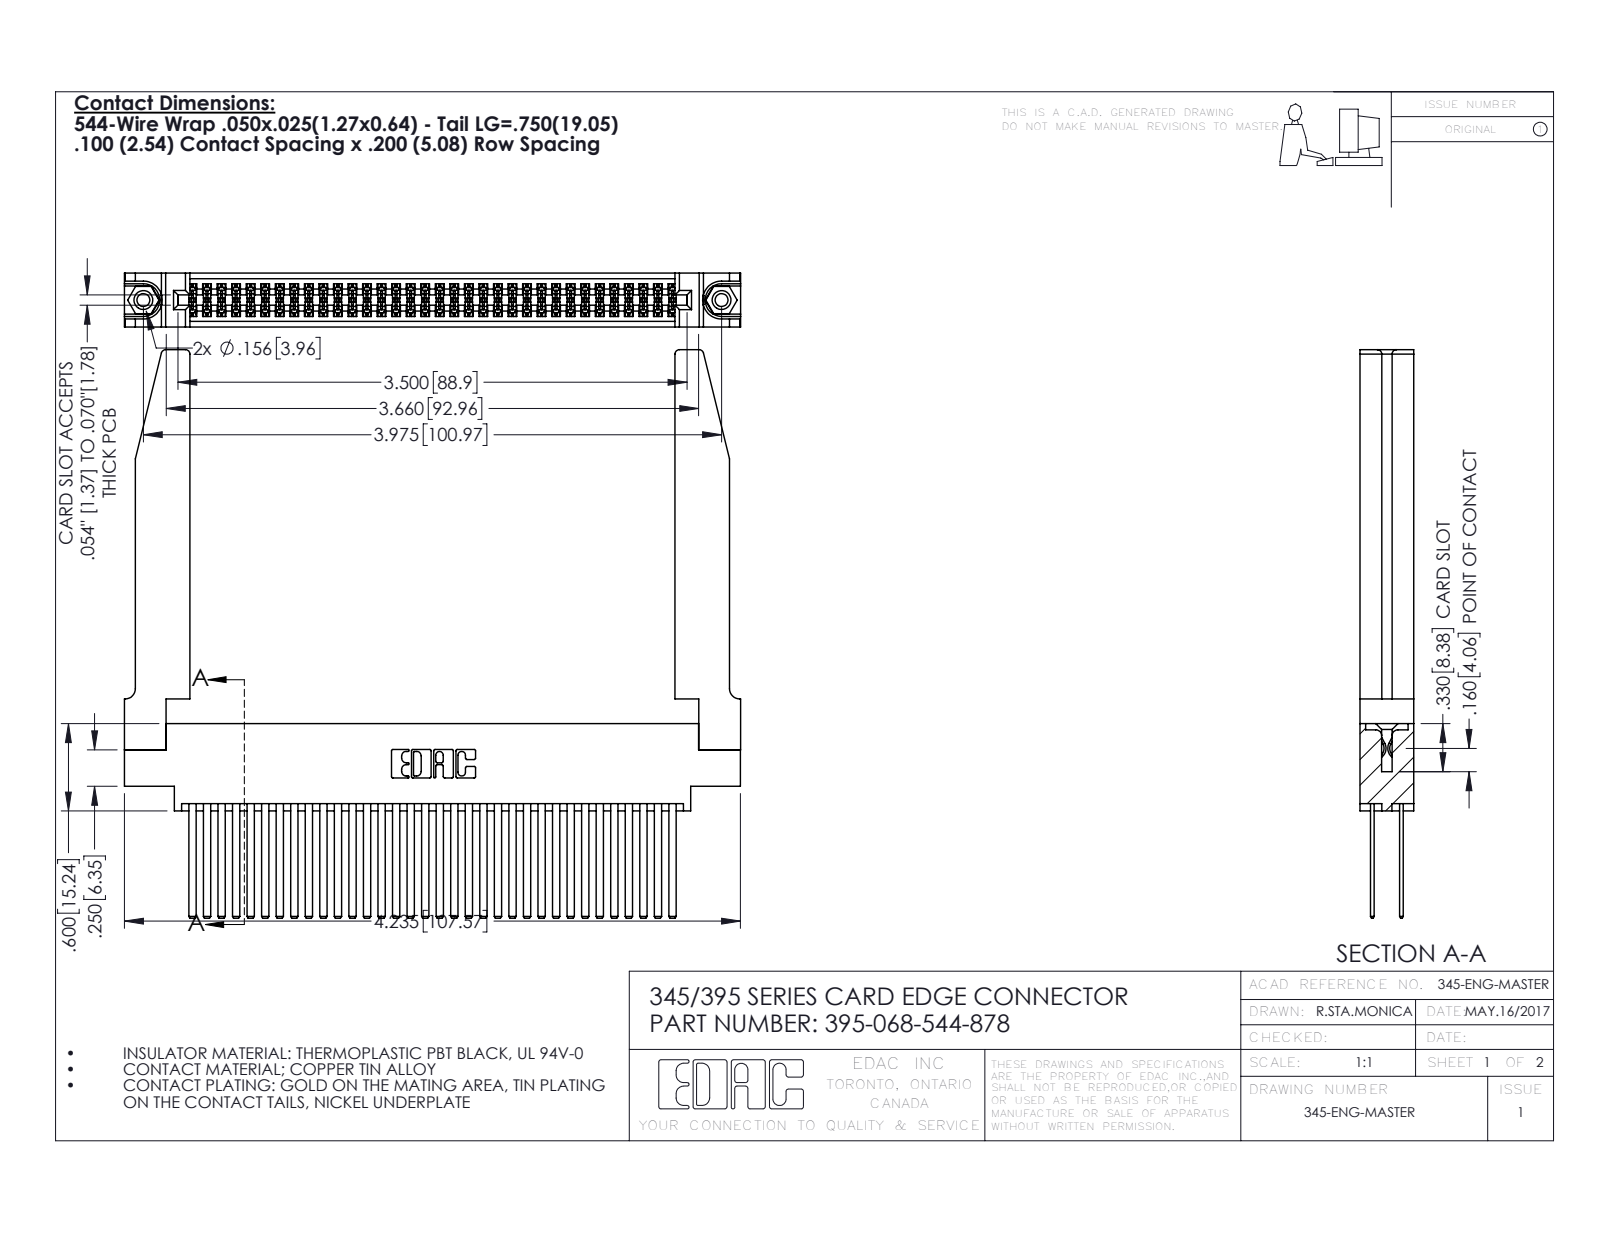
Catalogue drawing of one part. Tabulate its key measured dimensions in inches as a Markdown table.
| quantity | value |
| --- | --- |
| part name | 395-068-544-878; 345 Part_0.170 Offset - 0.156 Dia-TH; 345-292-001_345-293-144; 345-220-078_345-220-078 (+1 more) |
| STEP written by | SolidWorks 2016 (CONFIG_CONTROL_DESIGN) |
| units | inches |
| bodies | 73 solids, 3356 faces (2198 planar, 1106 cylindrical, 52 other) |
| overall size | 4.236 × 3.907 × 0.37 |
| volume | 1.159 in³ |
| surface area | 40.61 in² |
| round holes (diameter × count) | 0.089 × 2, 0.125 × 2, 0.156 × 2, 0.064 × 1 |
| round bosses / shafts (diameter × count) | 0.155 × 2 |
| partial cylindrical surfaces (radius × count) | 0.006 × 102, 0.01 × 22, 0.03 × 8, 0.007 × 6, 0.031 × 6, 0.026 × 3, 0.014 × 2, 0.019 × 2 |
| main face-to-face distances | 0.072, 0.298, 0.098, 0.272, 0.025, 0.2, 0.37, 0.225, 0.175, 0.15 |
| hole center spacings | 0.27, 3.74, 3.975 |
